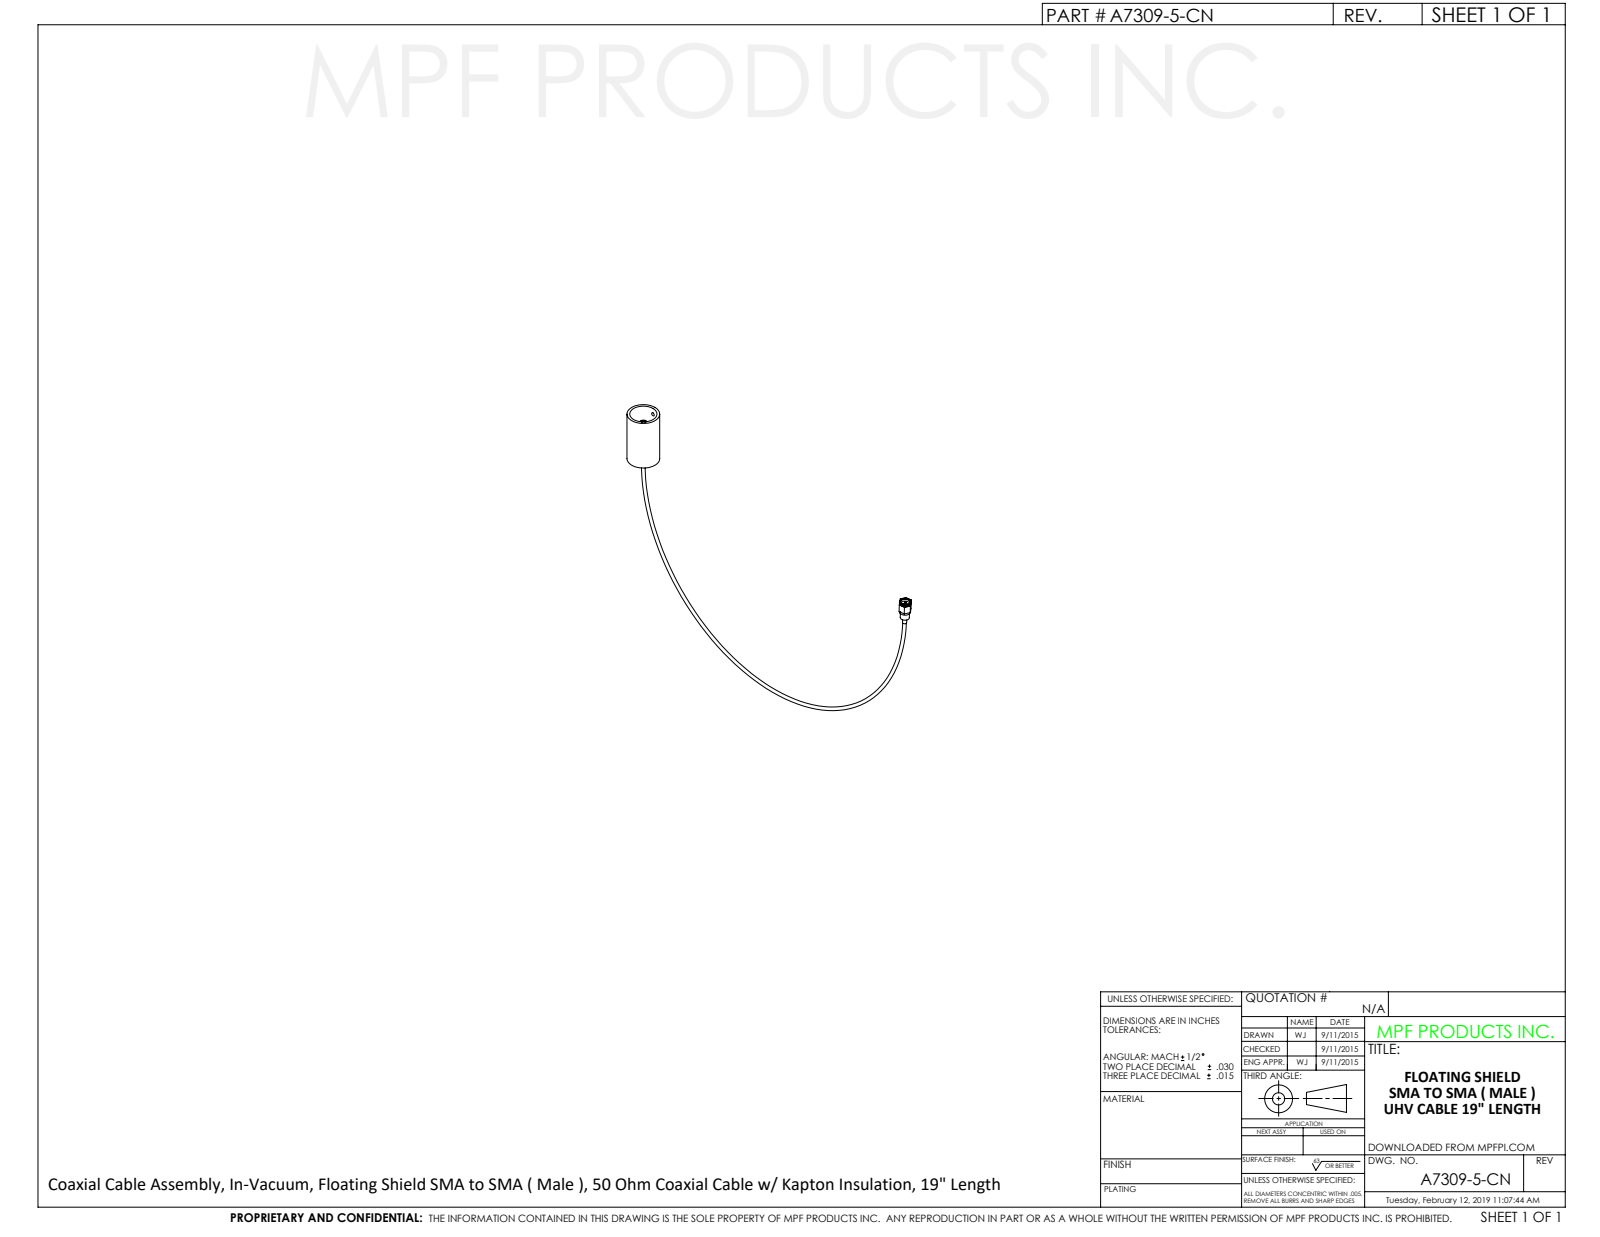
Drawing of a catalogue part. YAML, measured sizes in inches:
part_name: "A7309-1-CN_110183; A7309-5-CN; A7300 MALE SMA PART"
step_written_by: "SolidWorks 2012 (CONFIG_CONTROL_DESIGN)"
units: inches
bodies: {solids: 3, faces: 122, planar: 57, cylindrical: 58, other: 7}
overall_size: [10.865, 6.833, 1]
volume: 1.018
surface_area: 15.29
round_holes:
  - {diameter: 0.1, count: 3}
  - {diameter: 0.05, count: 1}
  - {diameter: 0.115, count: 1}
  - {diameter: 0.167, count: 1}
  - {diameter: 0.186, count: 1}
  - {diameter: 0.2, count: 1}
  - {diameter: 0.257, count: 1}
  - {diameter: 0.293, count: 1}
  - {diameter: 0.75, count: 1}
round_bosses_or_shafts:
  - {diameter: 1, count: 1}
  - {diameter: 0.307, count: 1}
  - {diameter: 0.294, count: 1}
  - {diameter: 0.25, count: 1}
  - {diameter: 0.207, count: 1}
  - {diameter: 0.2, count: 1}
  - {diameter: 0.18, count: 1}
  - {diameter: 0.165, count: 1}
face_to_face_distances: [1.5, 0.308, 0.04, 0.308, 0.305, 0.214, 0.409, 0.104, 0.11, 0.195]
hole_center_spacings: [0.35]
